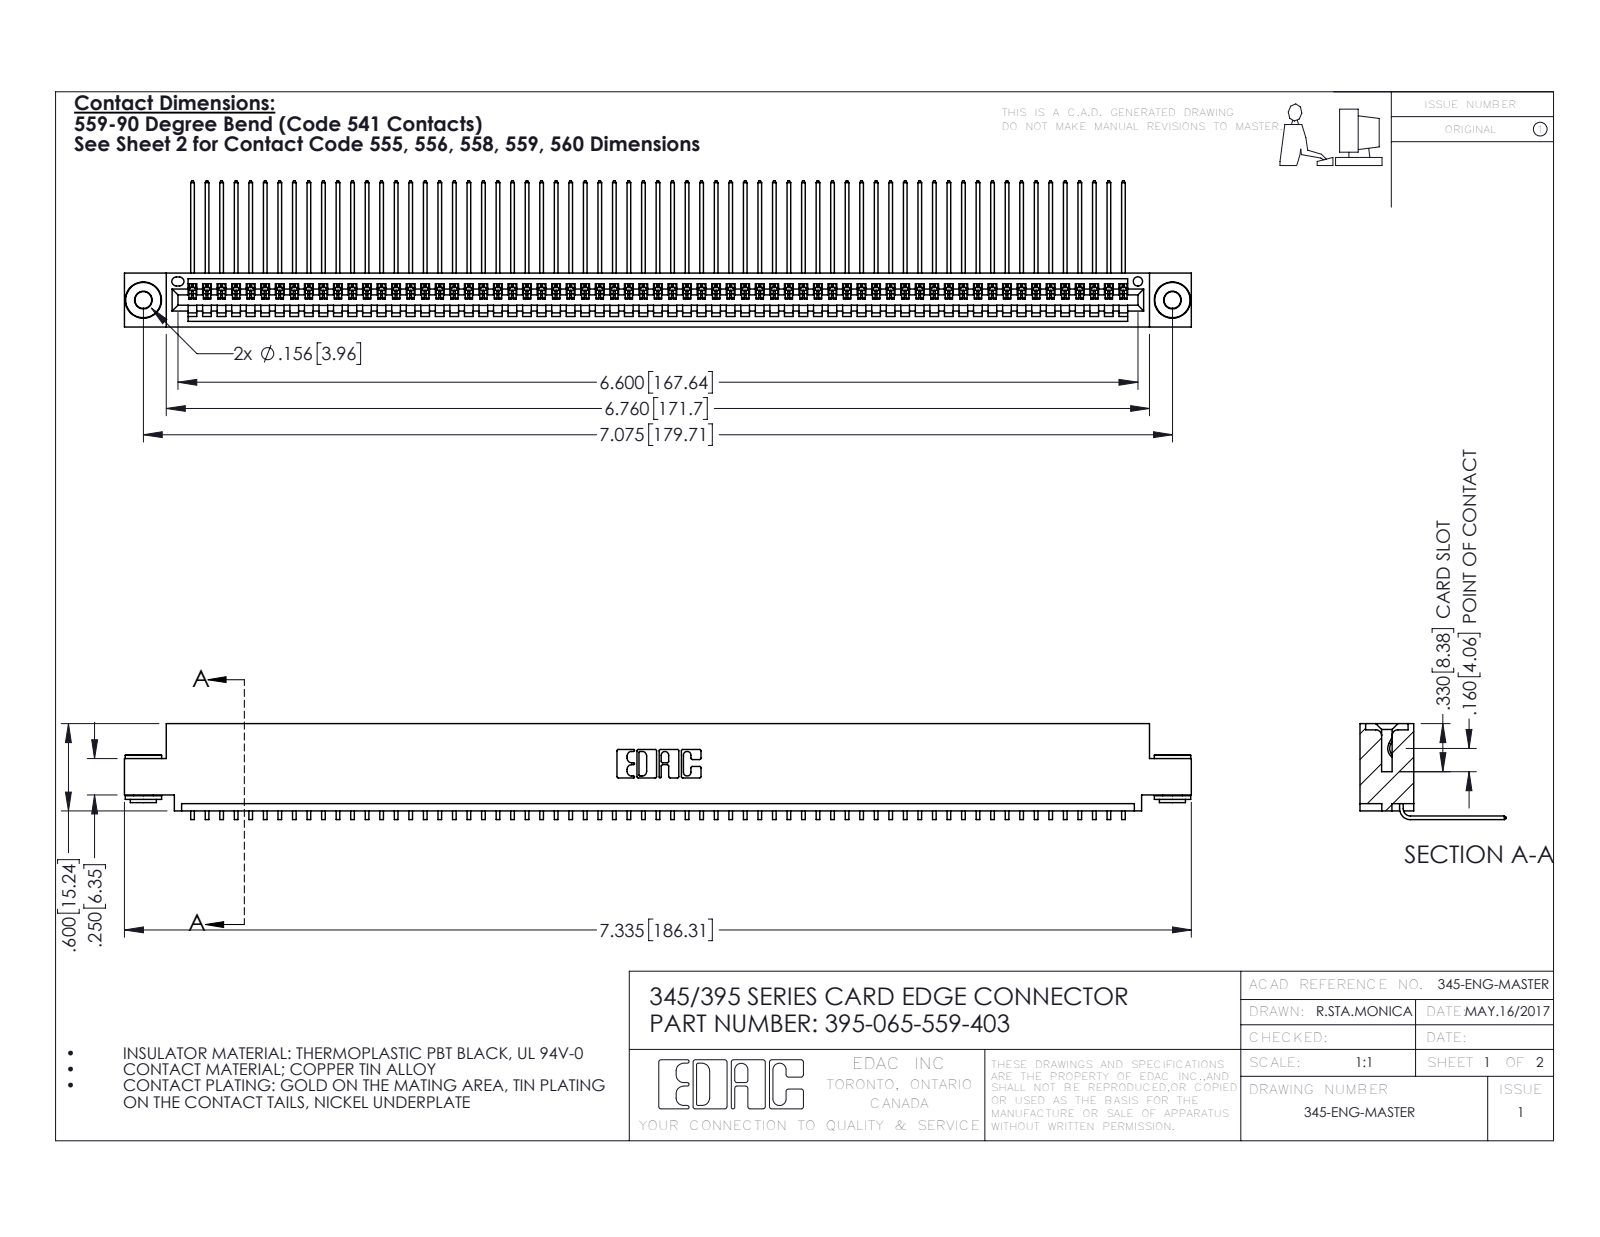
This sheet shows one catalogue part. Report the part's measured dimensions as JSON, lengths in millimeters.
{"part_name": "395-065-559-403; 345-250-002_345-250-002-102; 345-292-001_558 559 Tail - 1; 345 Part_0.110 Offset - 0.156 Dia-TH", "step_written_by": "SolidWorks 2016 (CONFIG_CONTROL_DESIGN)", "units": "millimeters", "bodies": {"solids": 68, "faces": 4068, "planar": 2824, "cylindrical": 1236, "other": 8}, "overall_size": [186.3, 25.5, 16.7], "volume_mm3": 18040, "surface_area_mm2": 25860, "round_holes": [[2.9, 2], [4, 2], [1.6, 1]], "round_bosses_or_shafts": [[6.4, 2], [4.6, 2], [3.5, 2]], "partial_cylinders_radius": [[0.2, 130], [0.3, 22], [0.2, 6], [0.8, 6], [0.7, 3], [0.8, 2], [1, 2], [0.4, 1]], "face_to_face_distances": [1.8, 7.6, 9.4, 5.1, 0.6, 2.5, 6.9, 5.7, 3.8, 1.8], "hole_center_spacings": [6.9, 173.7, 179.7]}
